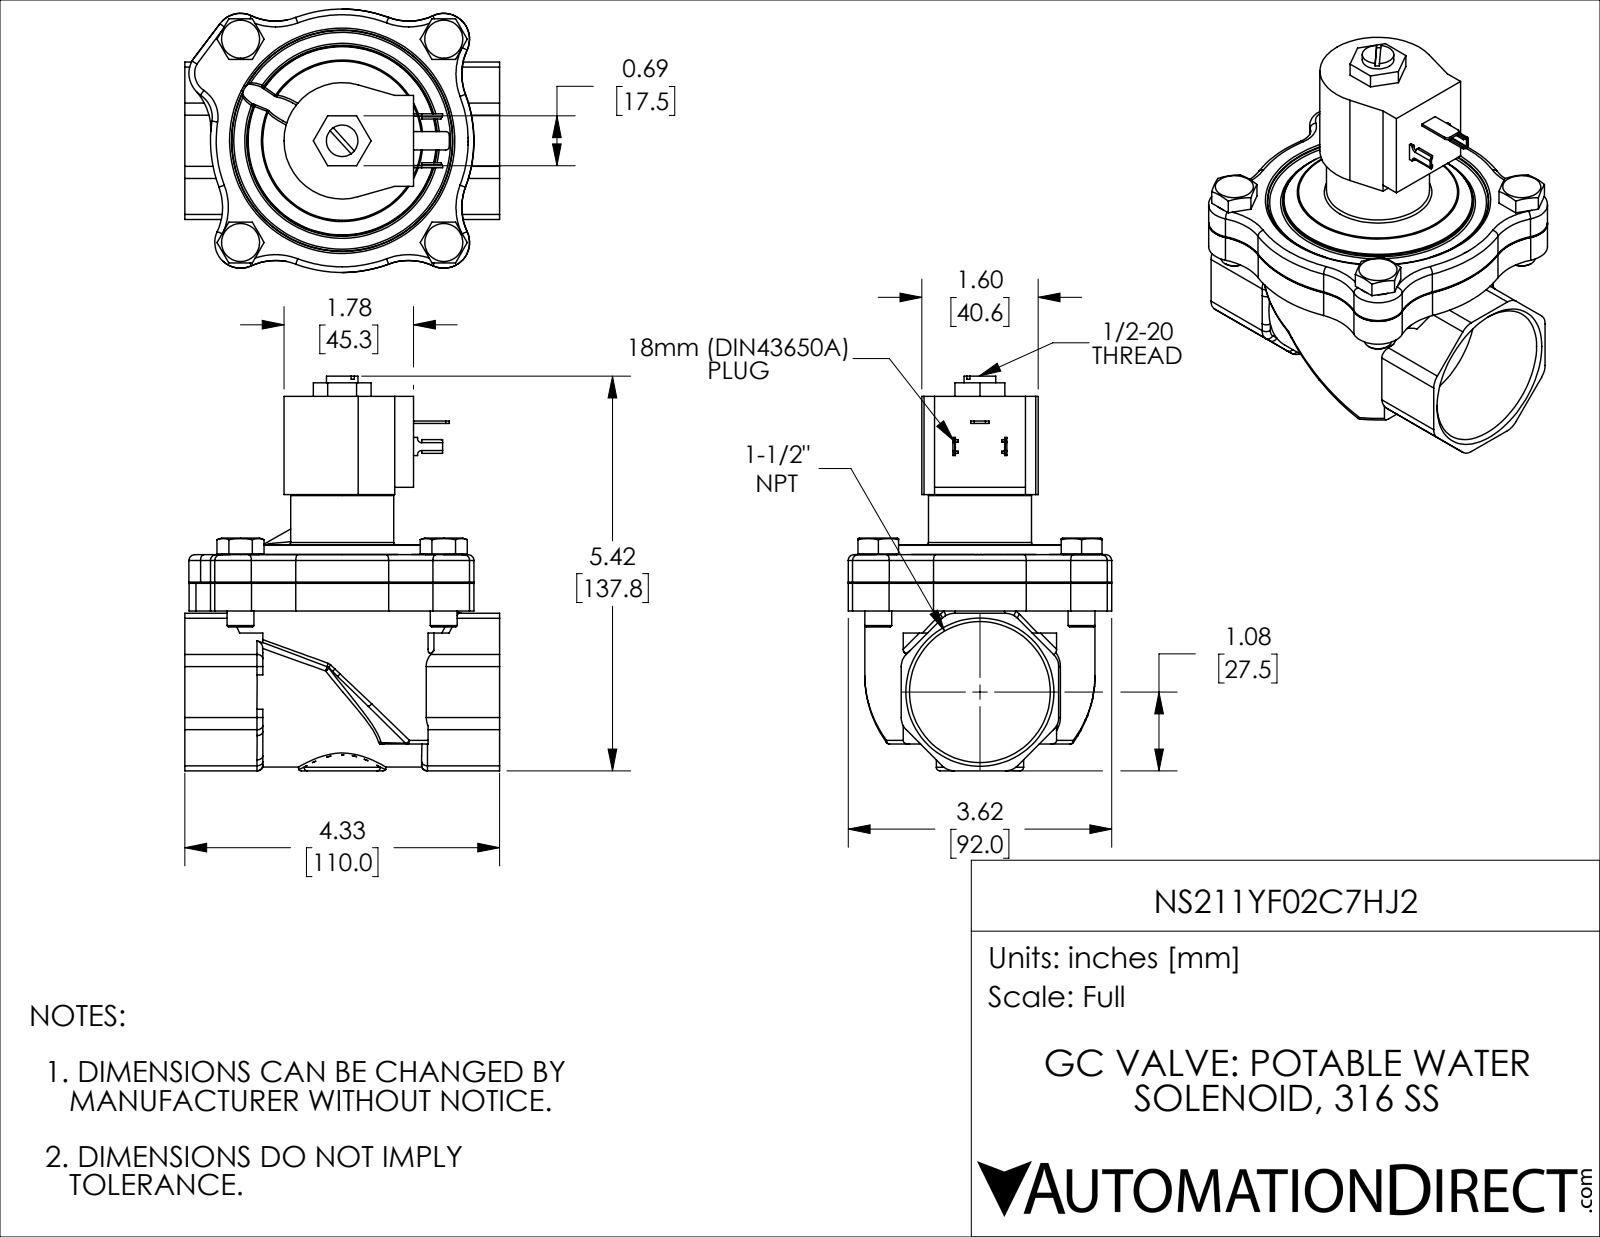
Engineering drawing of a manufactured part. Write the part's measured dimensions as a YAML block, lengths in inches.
part_name: "NS211YF02C7HJ2"
step_written_by: "SolidWorks 2018 (AUTOMOTIVE_DESIGN)"
units: inches
bodies: {solids: 9, faces: 520, planar: 159, cylindrical: 158, other: 203}
overall_size: [5.424, 4.33, 3.622]
volume: 25.63
surface_area: 136.4
round_holes:
  - {diameter: 0.375, count: 4}
  - {diameter: 0.433, count: 4}
  - {diameter: 0.125, count: 1}
  - {diameter: 0.434, count: 1}
  - {diameter: 0.846, count: 1}
  - {diameter: 0.949, count: 1}
  - {diameter: 1.937, count: 1}
round_bosses_or_shafts:
  - {diameter: 0.504, count: 4}
  - {diameter: 0.37, count: 4}
  - {diameter: 3.165, count: 1}
  - {diameter: 1.417, count: 1}
  - {diameter: 1.2, count: 1}
partial_cylinders:
  - {radius: 0.787, count: 15}
  - {radius: 0.08, count: 13}
  - {radius: 0.236, count: 8}
  - {radius: 0.354, count: 8}
  - {radius: 0.006, count: 4}
  - {radius: 0.041, count: 4}
  - {radius: 0.05, count: 2}
  - {radius: 0.06, count: 2}
face_to_face_distances: [0.382, 0.775, 0.393, 1.83, 1.602, 1.22, 0.827, 2.952, 2.57, 2.177]
hole_center_spacings: [2.795, 1.976, 1.977, 2.794, 2.795, 3.952, 3.953]
